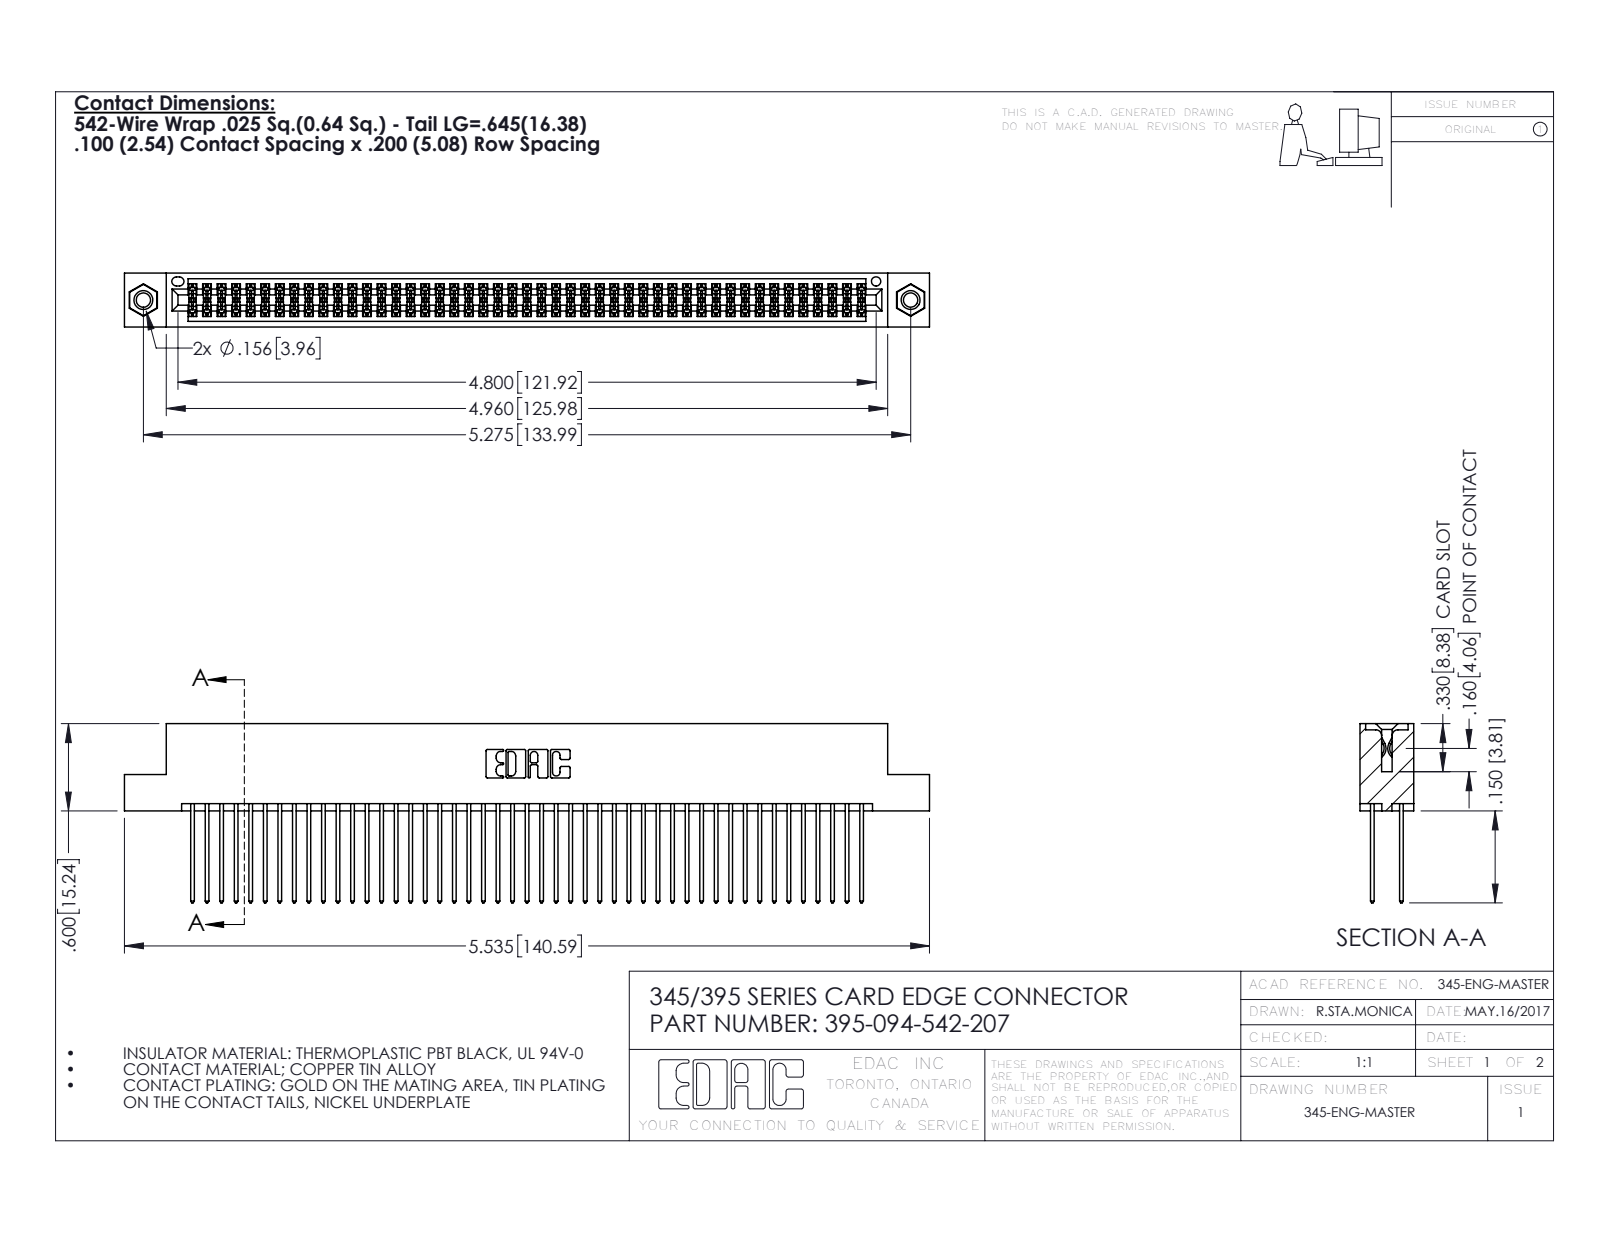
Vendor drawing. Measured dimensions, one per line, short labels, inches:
name: 345-250-001_345-250-005-103; 345-292-001_345-293-142; 395-094-542-207; 345 Part_Flush Mounting Lugs - 0.156 Dia-TI
written by: SolidWorks 2016 (CONFIG_CONTROL_DESIGN)
unit: in
bodies: 97 solids, 4886 faces (3214 planar, 1656 cylindrical, 16 other)
size: 5.535 × 1.232 × 0.37
volume: 0.862 in³; area: 35.74 in²
holes: 2× ⌀0.098, 2× ⌀0.125, 2× ⌀0.156, 1× ⌀0.064
bosses: 2× ⌀0.155
rounds: 141× R0.006, 94× R0.01, 22× R0.01, 6× R0.007, 6× R0.031, 3× R0.026, 2× R0.014, 2× R0.019
face distances: 0.072, 0.298, 0.2, 0.098, 0.272, 0.025, 0.225, 0.37, 0.175, 0.149
hole spacings: 0.27, 5.039, 5.275
